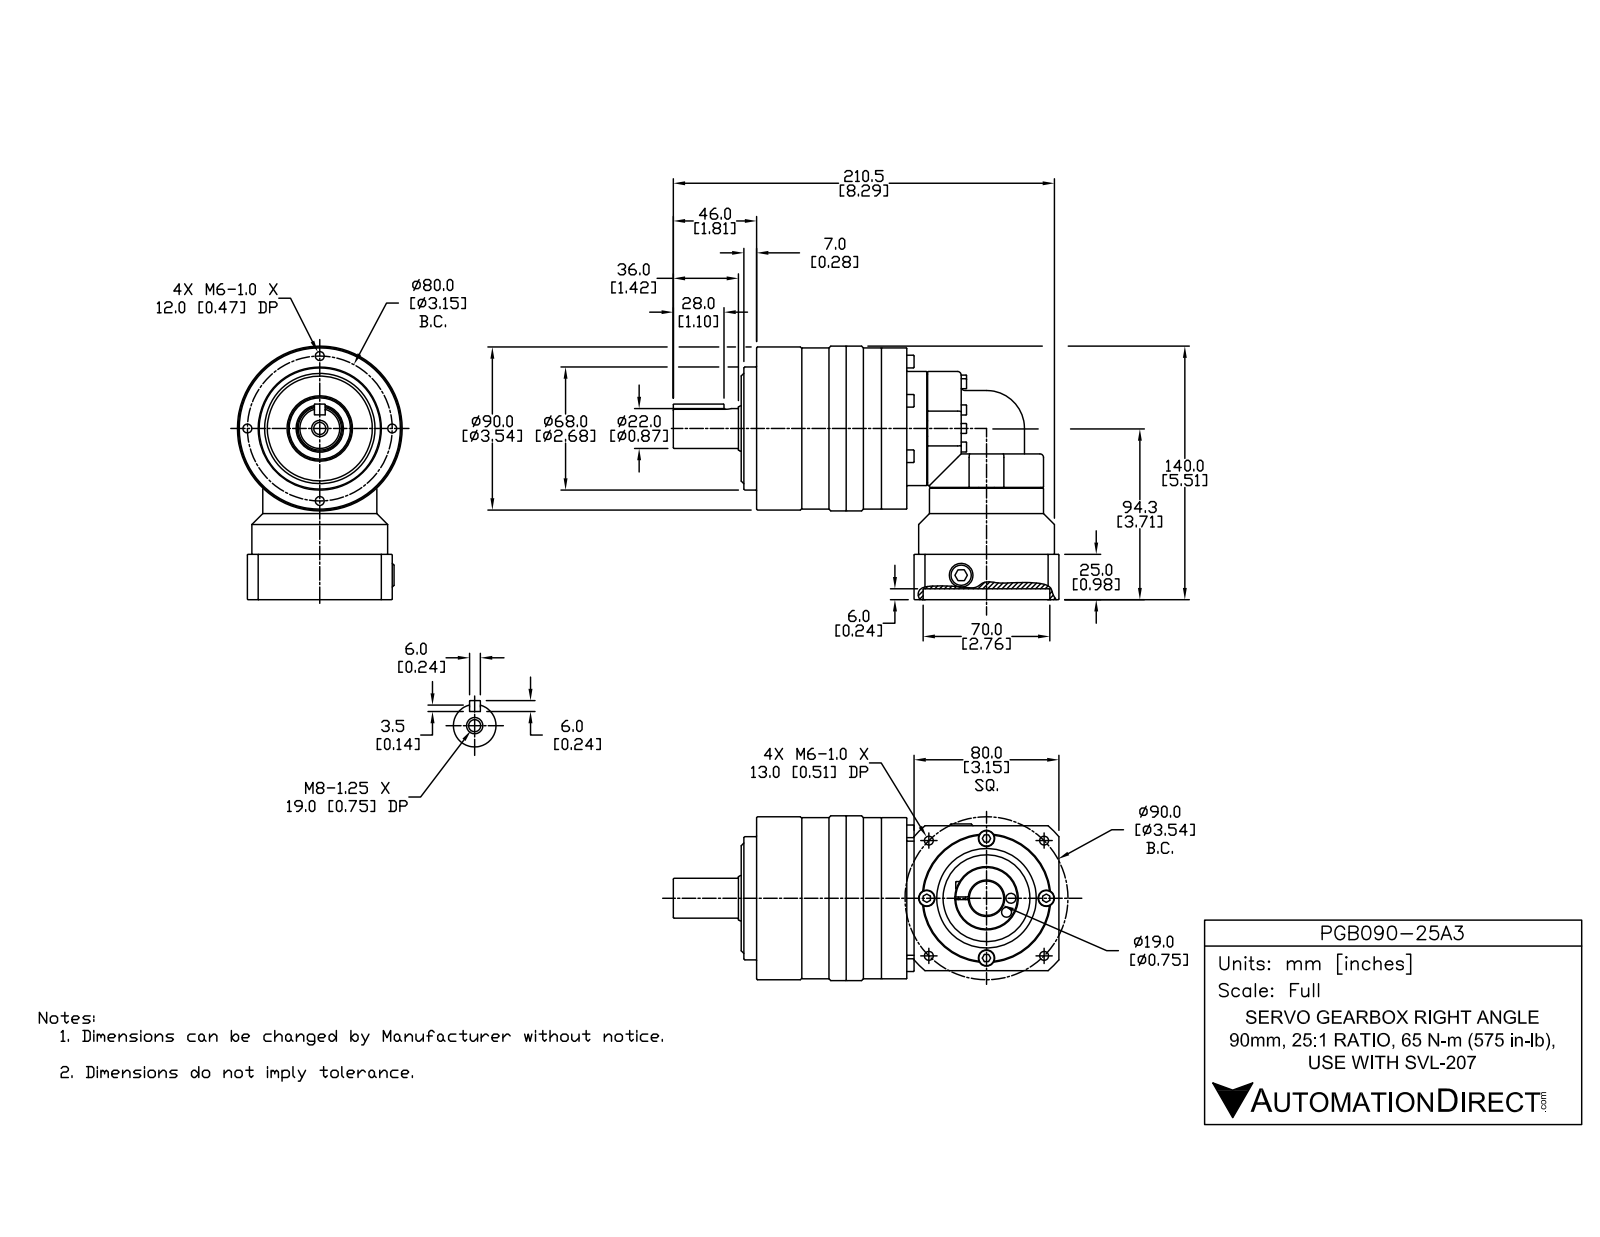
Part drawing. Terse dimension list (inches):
name: PGB090-25A3
written by: SolidWorks 2014 (AUTOMOTIVE_DESIGN)
unit: in
bodies: 1 solid, 642 faces (258 planar, 167 cylindrical, 217 other)
size: 8.386 × 5.512 × 3.583
volume: 59.64 in³; area: 144.1 in²
holes: 8× ⌀0.194, 7× ⌀0.177, 4× ⌀0.354, 2× ⌀0.217, 1× ⌀0.128, 1× ⌀0.262, 1× ⌀0.413, 1× ⌀0.748, 1× ⌀1.89, 1× ⌀2.165, 1× ⌀2.756
bosses: 9× ⌀0.217, 7× ⌀0.276, 7× ⌀0.157, 4× ⌀0.335, 2× ⌀2.48, 2× ⌀2.362, 1× ⌀3.583, 1× ⌀3.543
rounds: 6× R0.079, 2× R0.827, 1× R0.118, 1× R0.157, 1× R2.067
face distances: 3.15, 0.748, 3.268, 0.984, 0.236, 0.157, 0.335, 3.602, 3.425, 3.76
hole spacings: 1.254, 2.843, 0.615, 1.575, 1.75, 2.619, 3.089, 1.206
